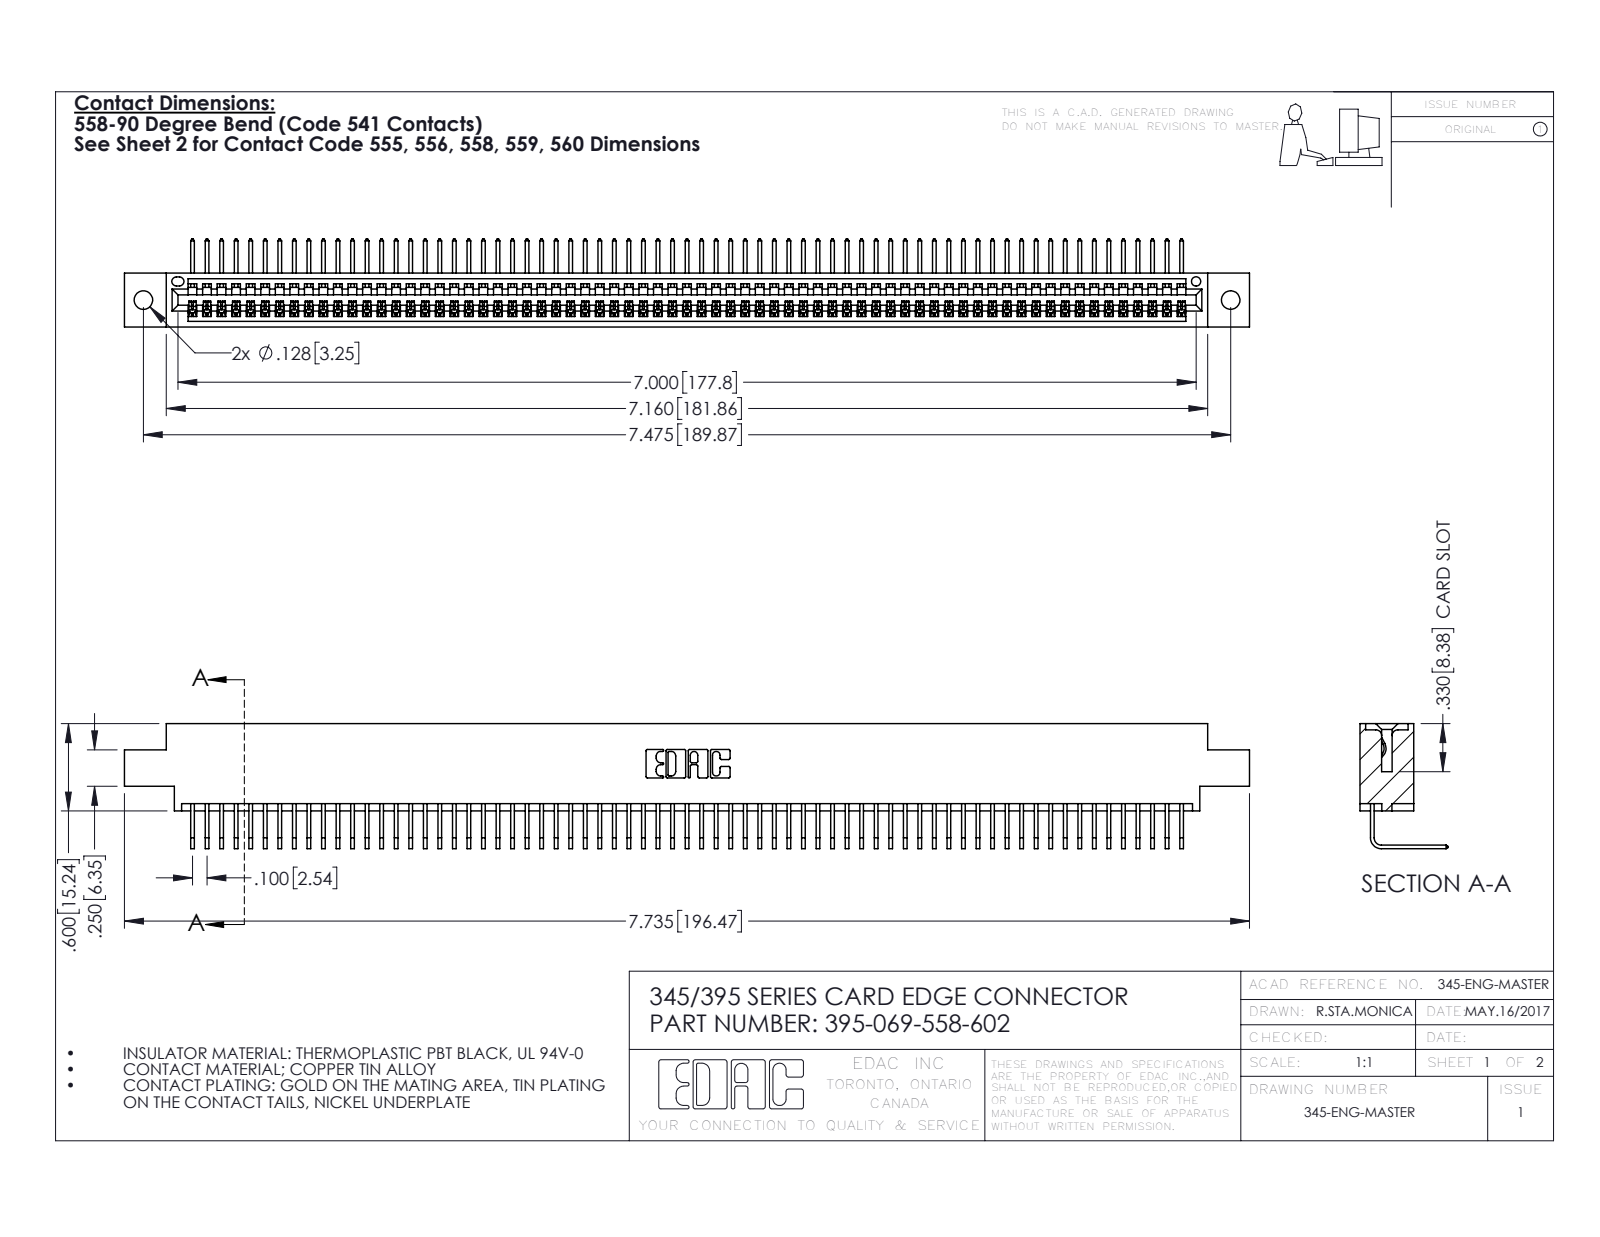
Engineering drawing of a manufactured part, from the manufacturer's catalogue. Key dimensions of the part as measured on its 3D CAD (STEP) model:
Part name (STEP PRODUCT): 395-069-558-602; 345-292-001_558 Tail - 2; 345 Part_0.170 Offset - 0.128 Dia
STEP written by: SolidWorks 2016 (CONFIG_CONTROL_DESIGN)
Units: inches
Bodies: 70 solids, 4270 faces (2982 planar, 1288 cylindrical, 0 other)
Overall size (bounding box): 7.735 × 0.859 × 0.605
Volume: 1.157 in³ · Surface area: 41.5 in²
Round holes (diameter × count): ⌀0.128 ×2, ⌀0.064 ×1
Partial cylindrical surfaces — rounded edges, fillets, slot ends (radius × count): R0.006 ×138, R0.01 ×22, R0.007 ×6, R0.031 ×6, R0.026 ×3, R0.031 ×2, R0.04 ×2, R0.014 ×1
Main face-to-face distances: 0.072, 0.298, 0.37, 0.2, 0.098, 0.272, 0.025, 0.225, 0.175, 0.149
Hole centre spacings: 0.27, 7.239, 7.475
